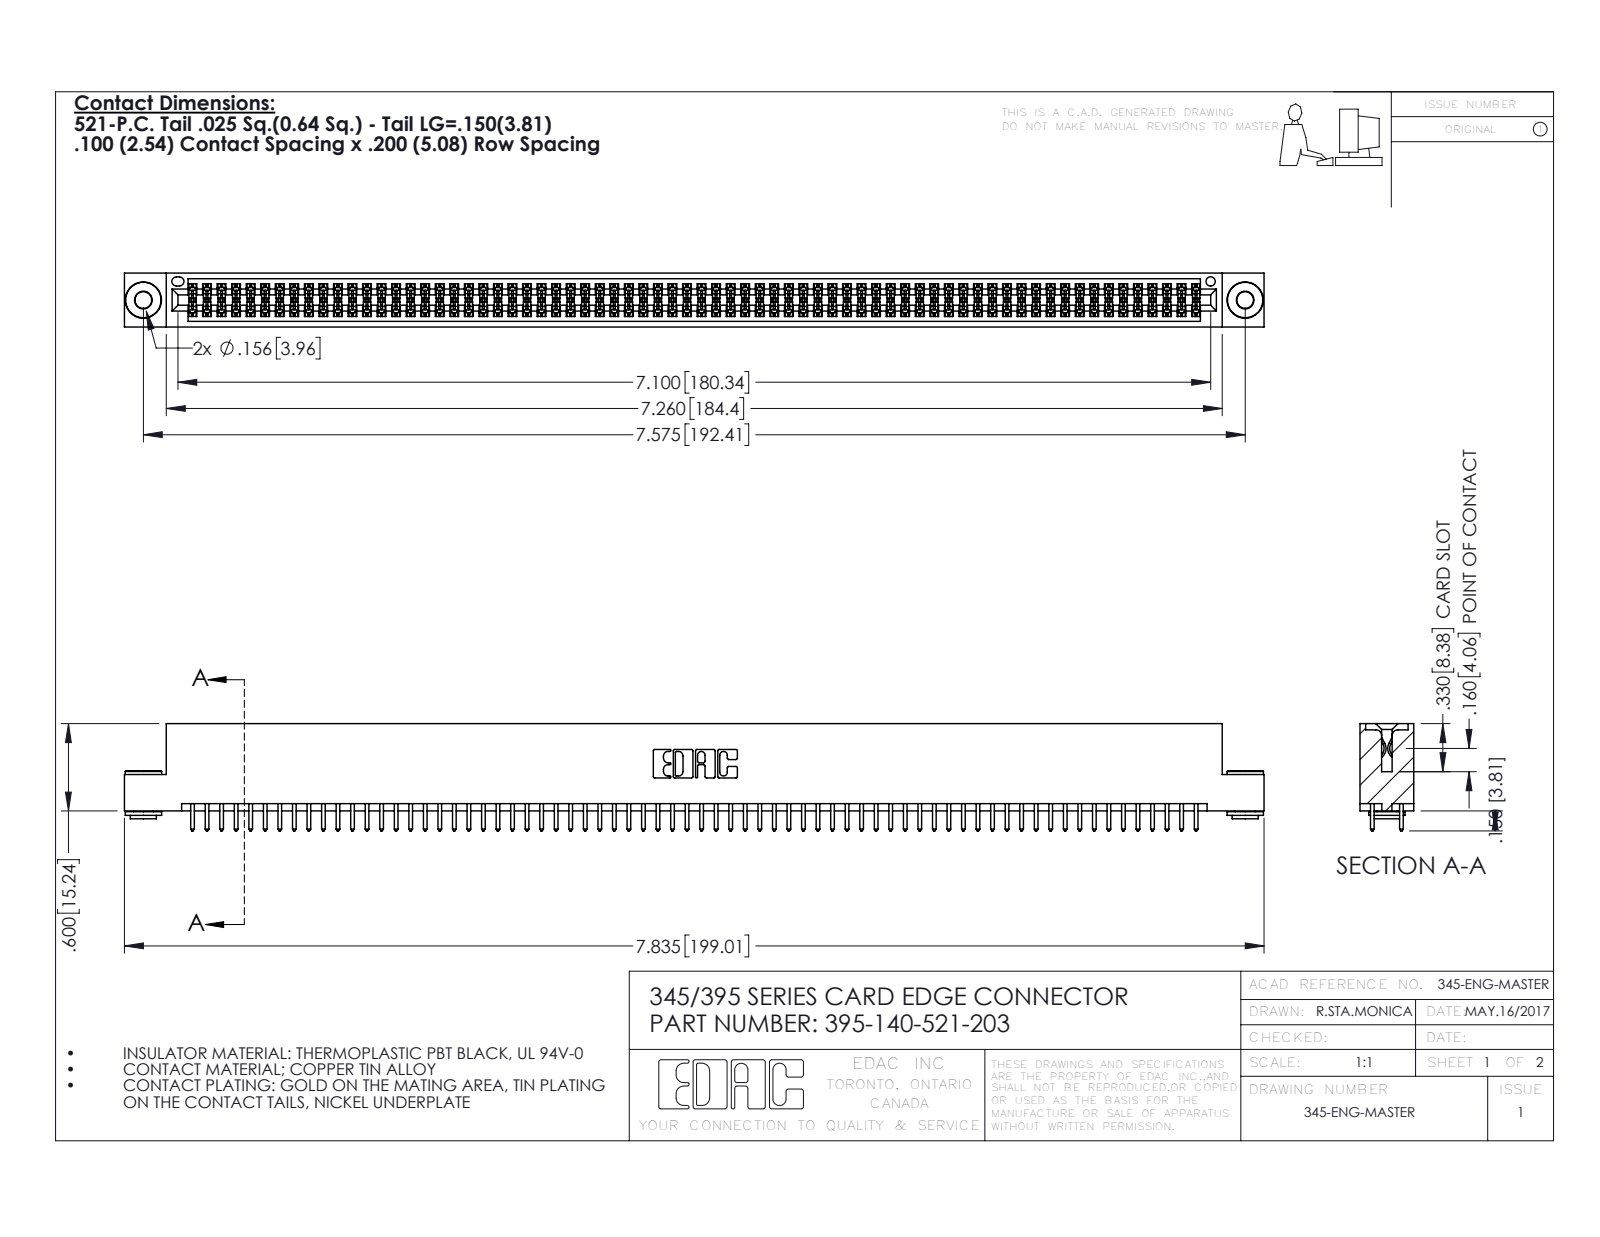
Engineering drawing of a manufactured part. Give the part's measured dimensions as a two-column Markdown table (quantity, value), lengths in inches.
| quantity | value |
| --- | --- |
| part name | 345 Part_Flush Mounting Lugs - 0.156 Dia-TH; 345-292-001_345-293-121; 395-140-521-203; 345-250-002_345-250-002-102 |
| STEP written by | SolidWorks 2016 (CONFIG_CONTROL_DESIGN) |
| units | inches |
| bodies | 143 solids, 7164 faces (4710 planar, 2446 cylindrical, 8 other) |
| overall size | 7.835 × 0.737 × 0.37 |
| volume | 1.193 in³ |
| surface area | 45.38 in² |
| round holes (diameter × count) | 0.116 × 2, 0.156 × 2, 0.064 × 1 |
| round bosses / shafts (diameter × count) | 0.25 × 2, 0.18 × 2, 0.136 × 2 |
| partial cylindrical surfaces (radius × count) | 0.006 × 210, 0.01 × 140, 0.01 × 22, 0.007 × 6, 0.031 × 6, 0.026 × 3, 0.014 × 2, 0.019 × 2 |
| main face-to-face distances | 0.072, 0.298, 0.2, 0.025, 0.098, 0.272, 0.37, 0.225, 0.175, 0.149 |
| hole center spacings | 0.27, 7.339, 7.575 |
